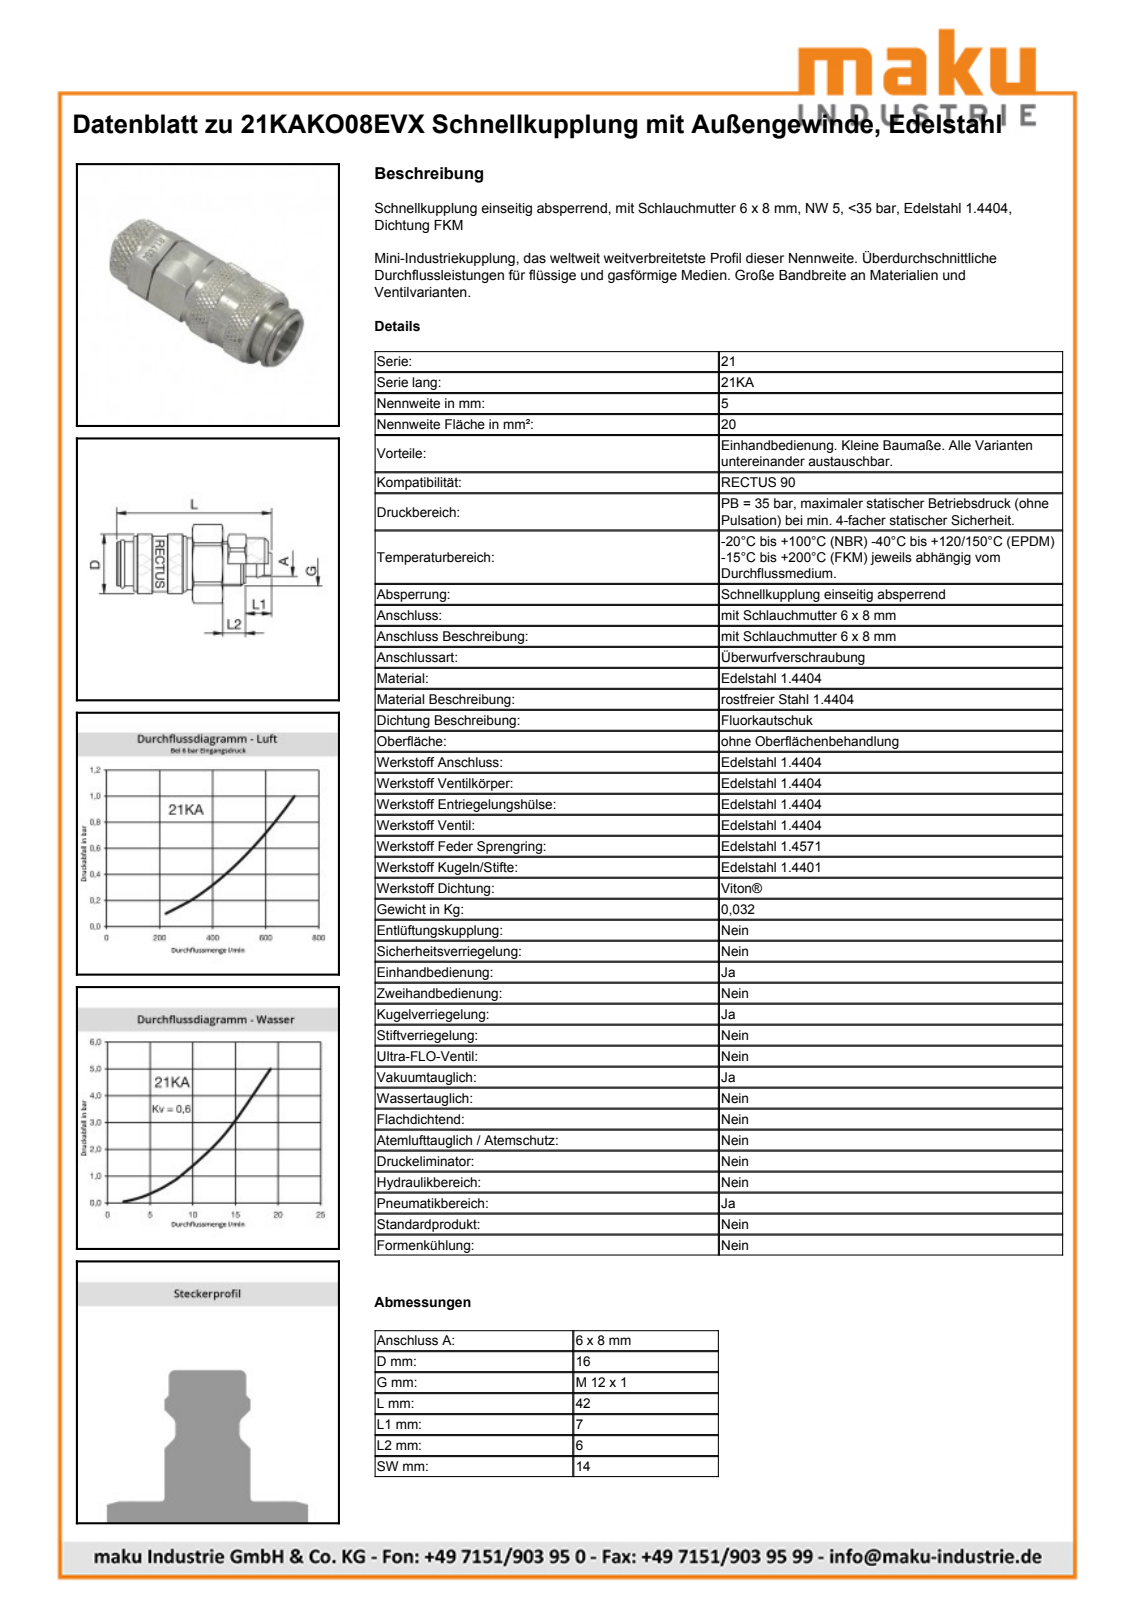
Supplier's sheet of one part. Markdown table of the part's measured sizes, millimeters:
| quantity | value |
| --- | --- |
| part name | D108445 |
| STEP written by | Autodesk Inventor 2013 (AUTOMOTIVE_DESIGN) |
| units | millimeters |
| bodies | 2 solids, 497 faces (158 planar, 68 cylindrical, 271 other) |
| overall size | 42.1 × 16.15 × 16.15 |
| volume | 6 191 mm³ |
| surface area | 4 116 mm² |
| round holes (diameter × count) | 8.25 × 1, 11.15 × 1, 12.15 × 1, 14 × 1 |
| round bosses / shafts (diameter × count) | 16.15 × 1, 15.1 × 1, 12 × 1, 11.4 × 1, 11.15 × 1, 10.6 × 1, 6.7 × 1, 6.05 × 1 |
| partial cylindrical surfaces (radius × count) | 7.45 × 1, 7.75 × 1, 7.9 × 1 |
| main face-to-face distances | 14, 35, 39.9, 4.9, 4.6, 30.4, 35.3, 11.9, 7.3, 23.1 |
